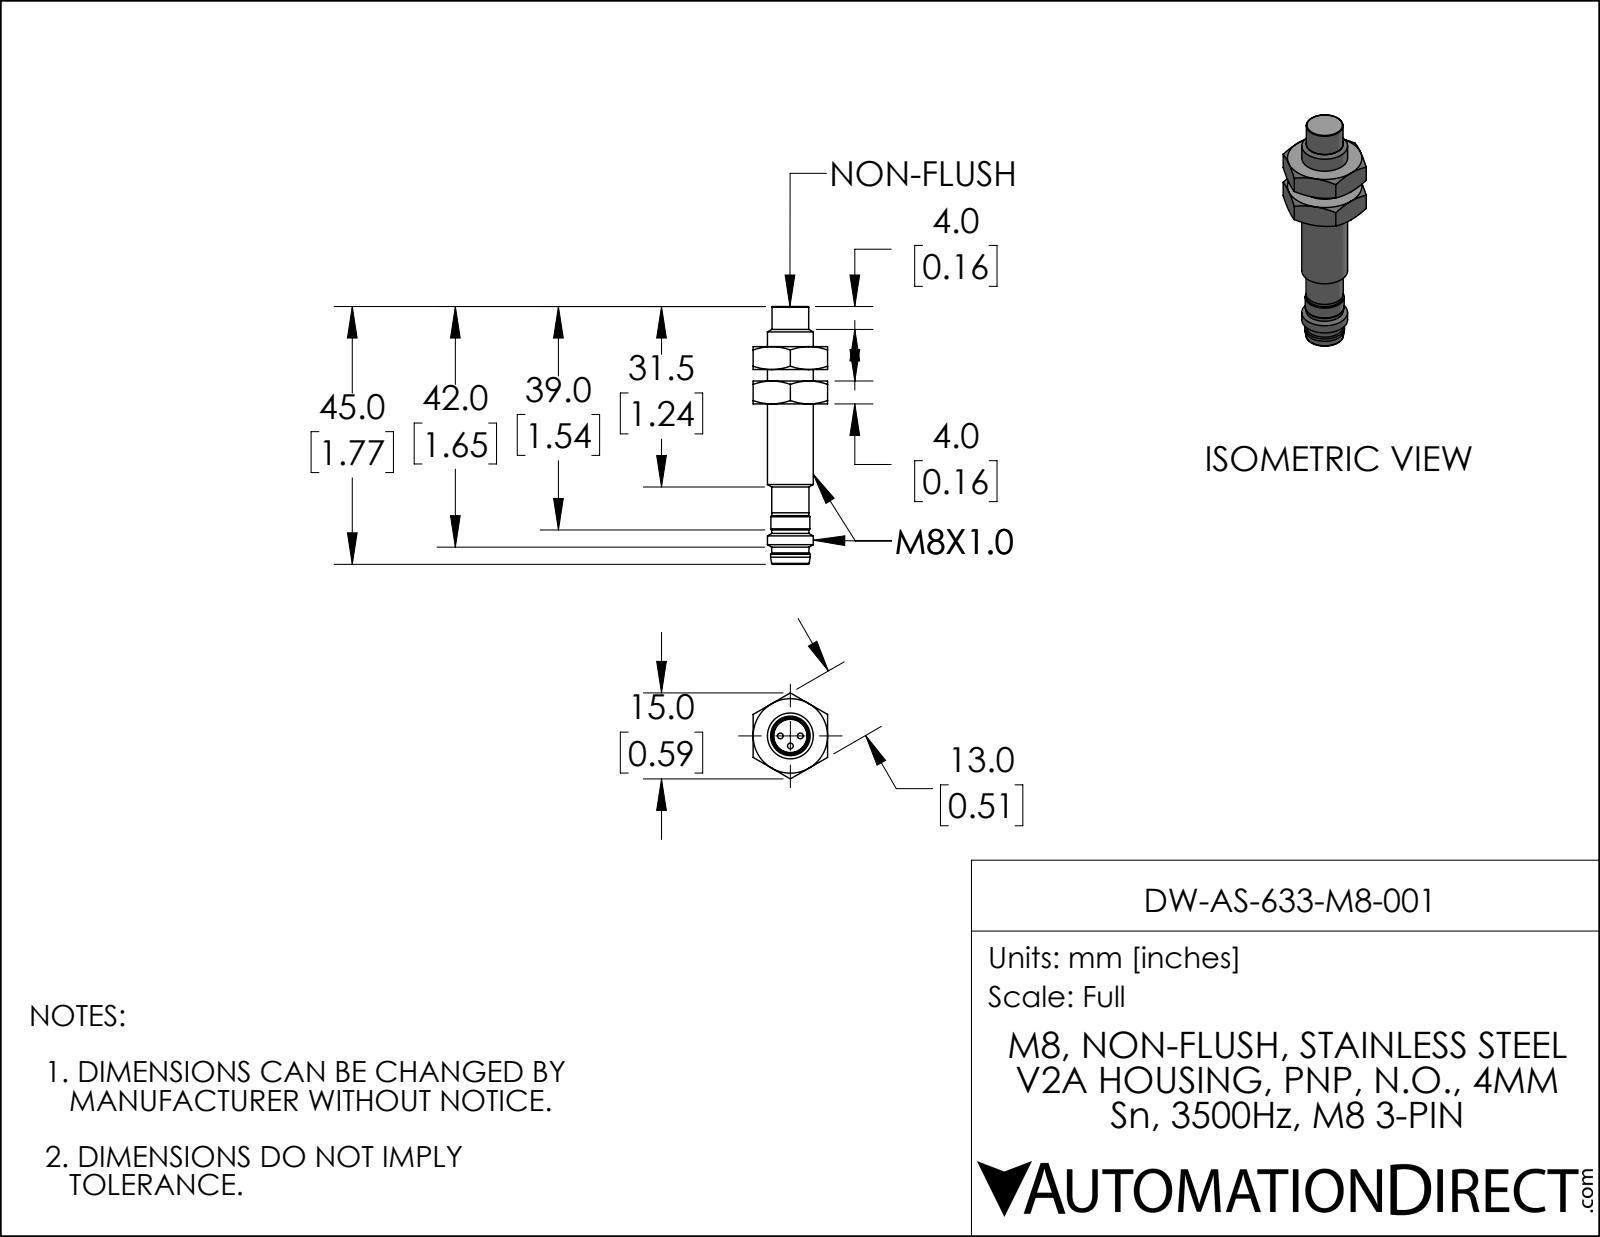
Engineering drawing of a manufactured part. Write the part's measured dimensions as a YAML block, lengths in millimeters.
part_name: "DW-AS-633-M8-001"
step_written_by: "SolidWorks 2019 (AUTOMOTIVE_DESIGN)"
units: millimeters
bodies: {solids: 1, faces: 76, planar: 24, cylindrical: 15, other: 37}
overall_size: [45, 15, 13]
volume: 2640
surface_area: 1817
round_holes:
  - {diameter: 5.8, count: 1}
round_bosses_or_shafts:
  - {diameter: 1, count: 3}
  - {diameter: 8, count: 1}
  - {diameter: 6.9, count: 1}
  - {diameter: 6.8, count: 1}
  - {diameter: 6.5, count: 1}
  - {diameter: 6.5, count: 1}
  - {diameter: 6.4, count: 1}
face_to_face_distances: [13, 4, 6, 2, 10, 7, 11, 17, 29, 23]
